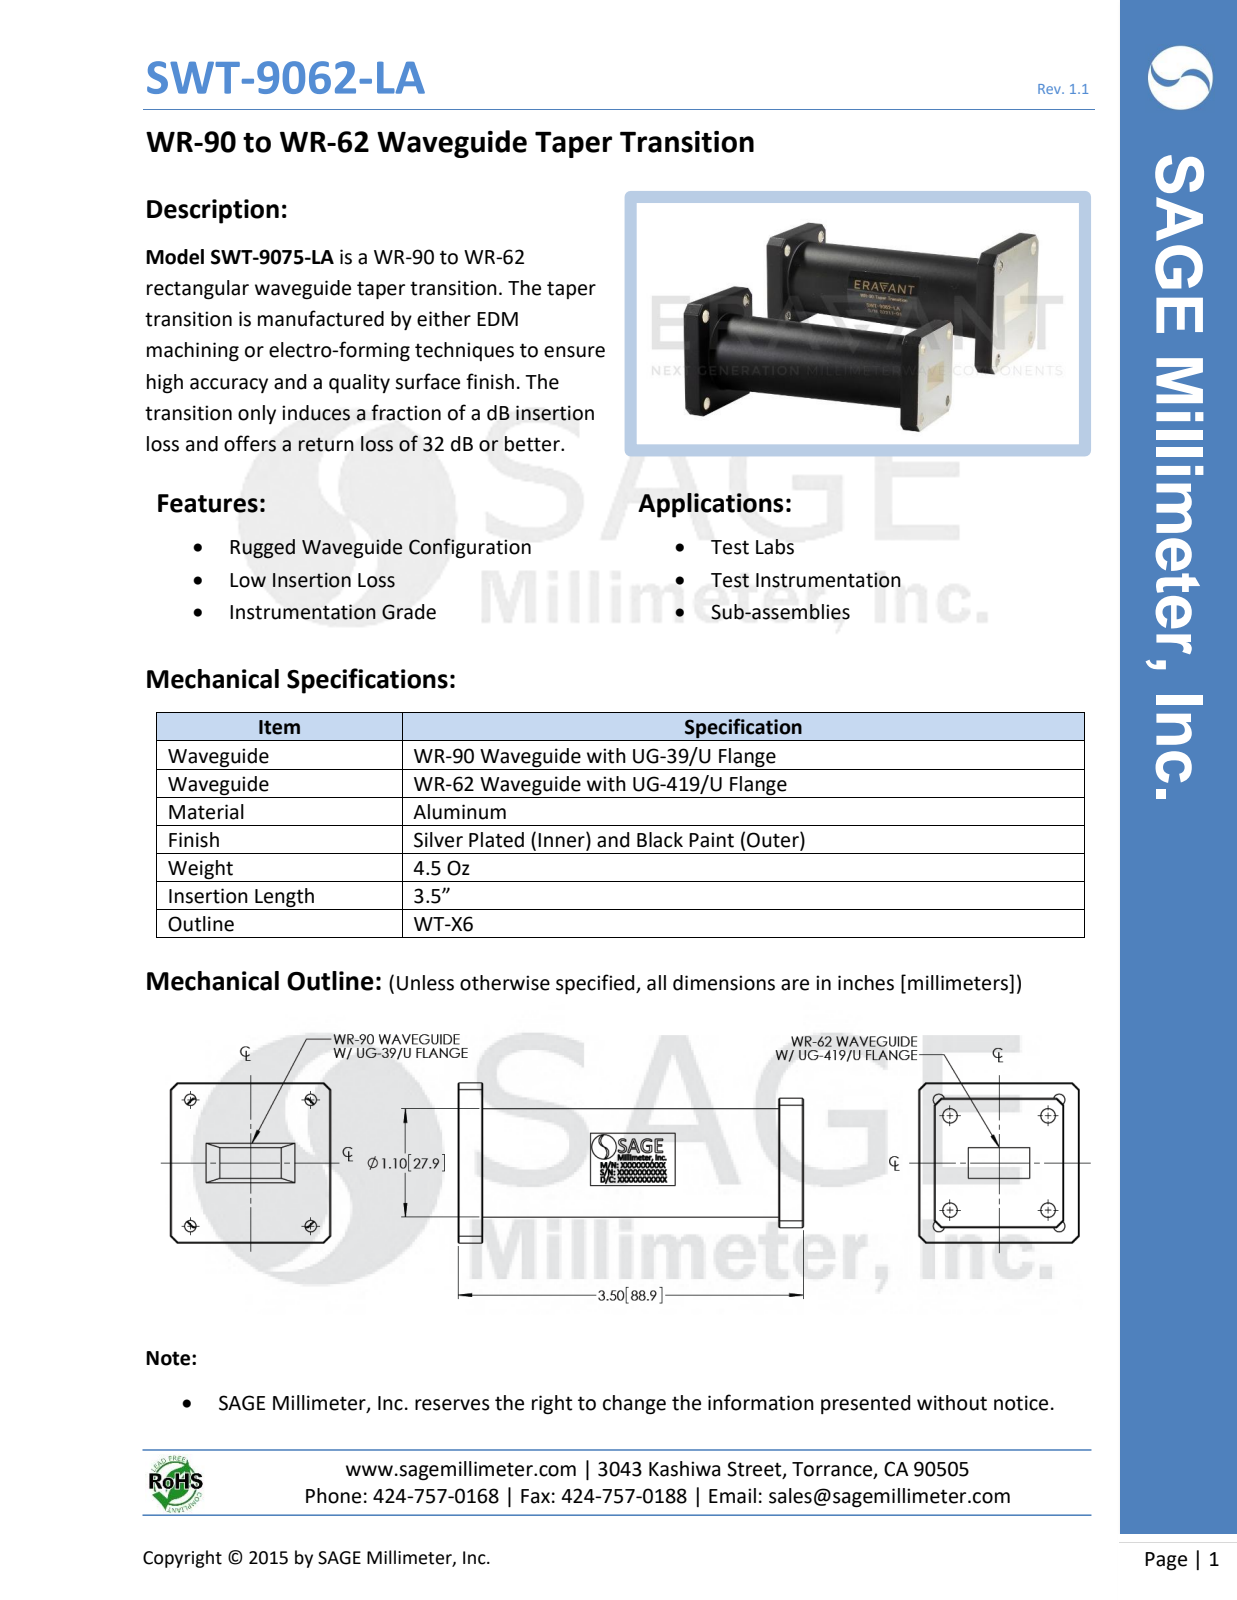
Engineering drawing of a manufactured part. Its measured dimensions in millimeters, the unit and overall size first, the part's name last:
Units: millimetres
Overall size (bounding box): 88.9 × 41.3 × 41.3
Round holes (diameter × count): ⌀3.7 ×4, ⌀4.4 ×4
Round bosses / shafts (diameter × count): ⌀27.9 ×1
Main face-to-face distances: 6.4, 82.6, 88.9, 1.6, 39.7, 76.2, 41.3, 88.9, 6.3, 82.5
Hole centre spacings: 3, 28.8, 30.6, 41.9, 26.4, 28.5, 31, 32.5
Volume: 65 990 mm³ · Surface area: 14 060 mm²
Bodies: 1 solid, 80 faces (62 planar, 18 cylindrical, 0 other)
Part name (STEP PRODUCT): SWT-9075-LA
STEP written by: SolidWorks 2016 (AUTOMOTIVE_DESIGN)
